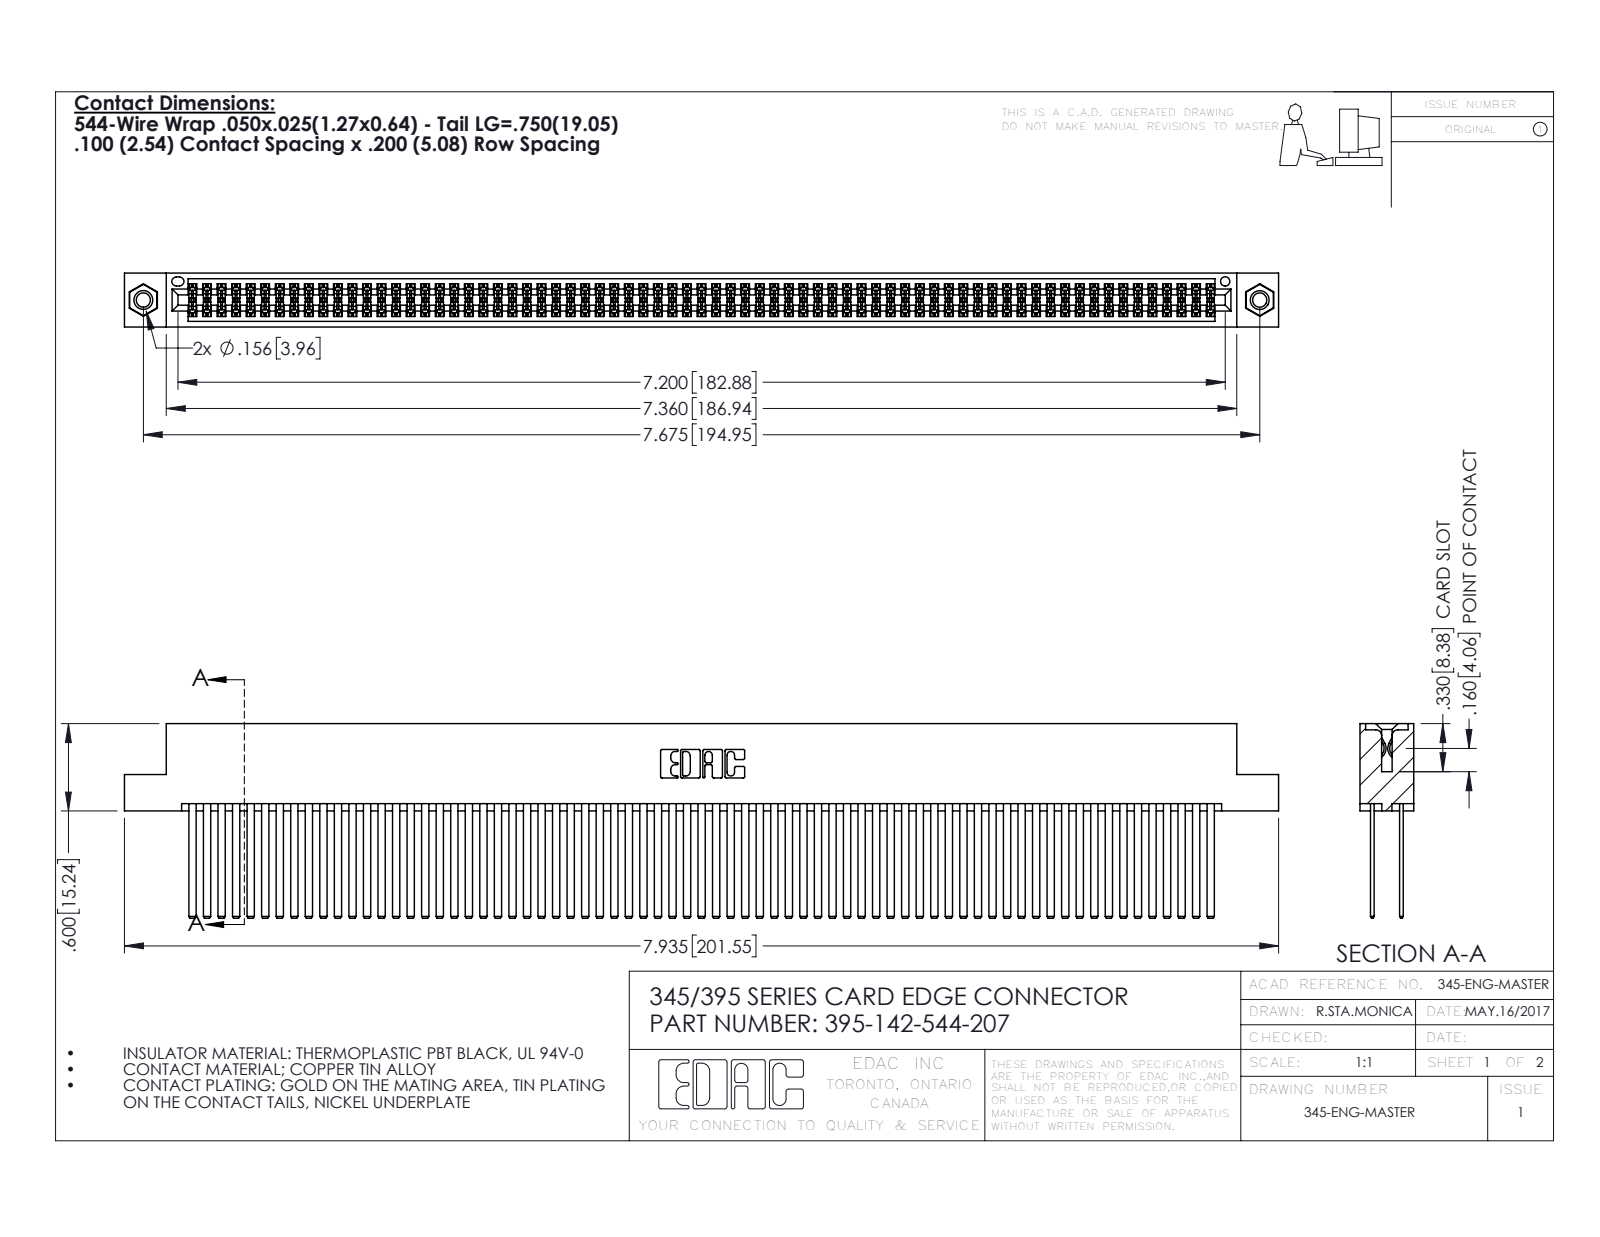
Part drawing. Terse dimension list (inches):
name: 345-292-001_345-293-144; 395-142-544-207; 345-250-001_345-250-005-103; 345 Part_Flush Mounting Lugs - 0.156 Dia-TI
written by: SolidWorks 2016 (CONFIG_CONTROL_DESIGN)
unit: in
bodies: 145 solids, 6434 faces (4230 planar, 2188 cylindrical, 16 other)
size: 7.935 × 1.337 × 0.37
volume: 1.332 in³; area: 59.96 in²
holes: 2× ⌀0.098, 2× ⌀0.125, 2× ⌀0.156, 1× ⌀0.064
bosses: 2× ⌀0.155
rounds: 213× R0.006, 22× R0.01, 6× R0.007, 6× R0.031, 3× R0.026, 2× R0.014, 2× R0.019, 2× R0.022
face distances: 0.2, 0.025, 0.072, 0.098, 0.272, 0.298, 0.225, 0.175, 0.37, 0.05
hole spacings: 0.27, 7.439, 7.675
